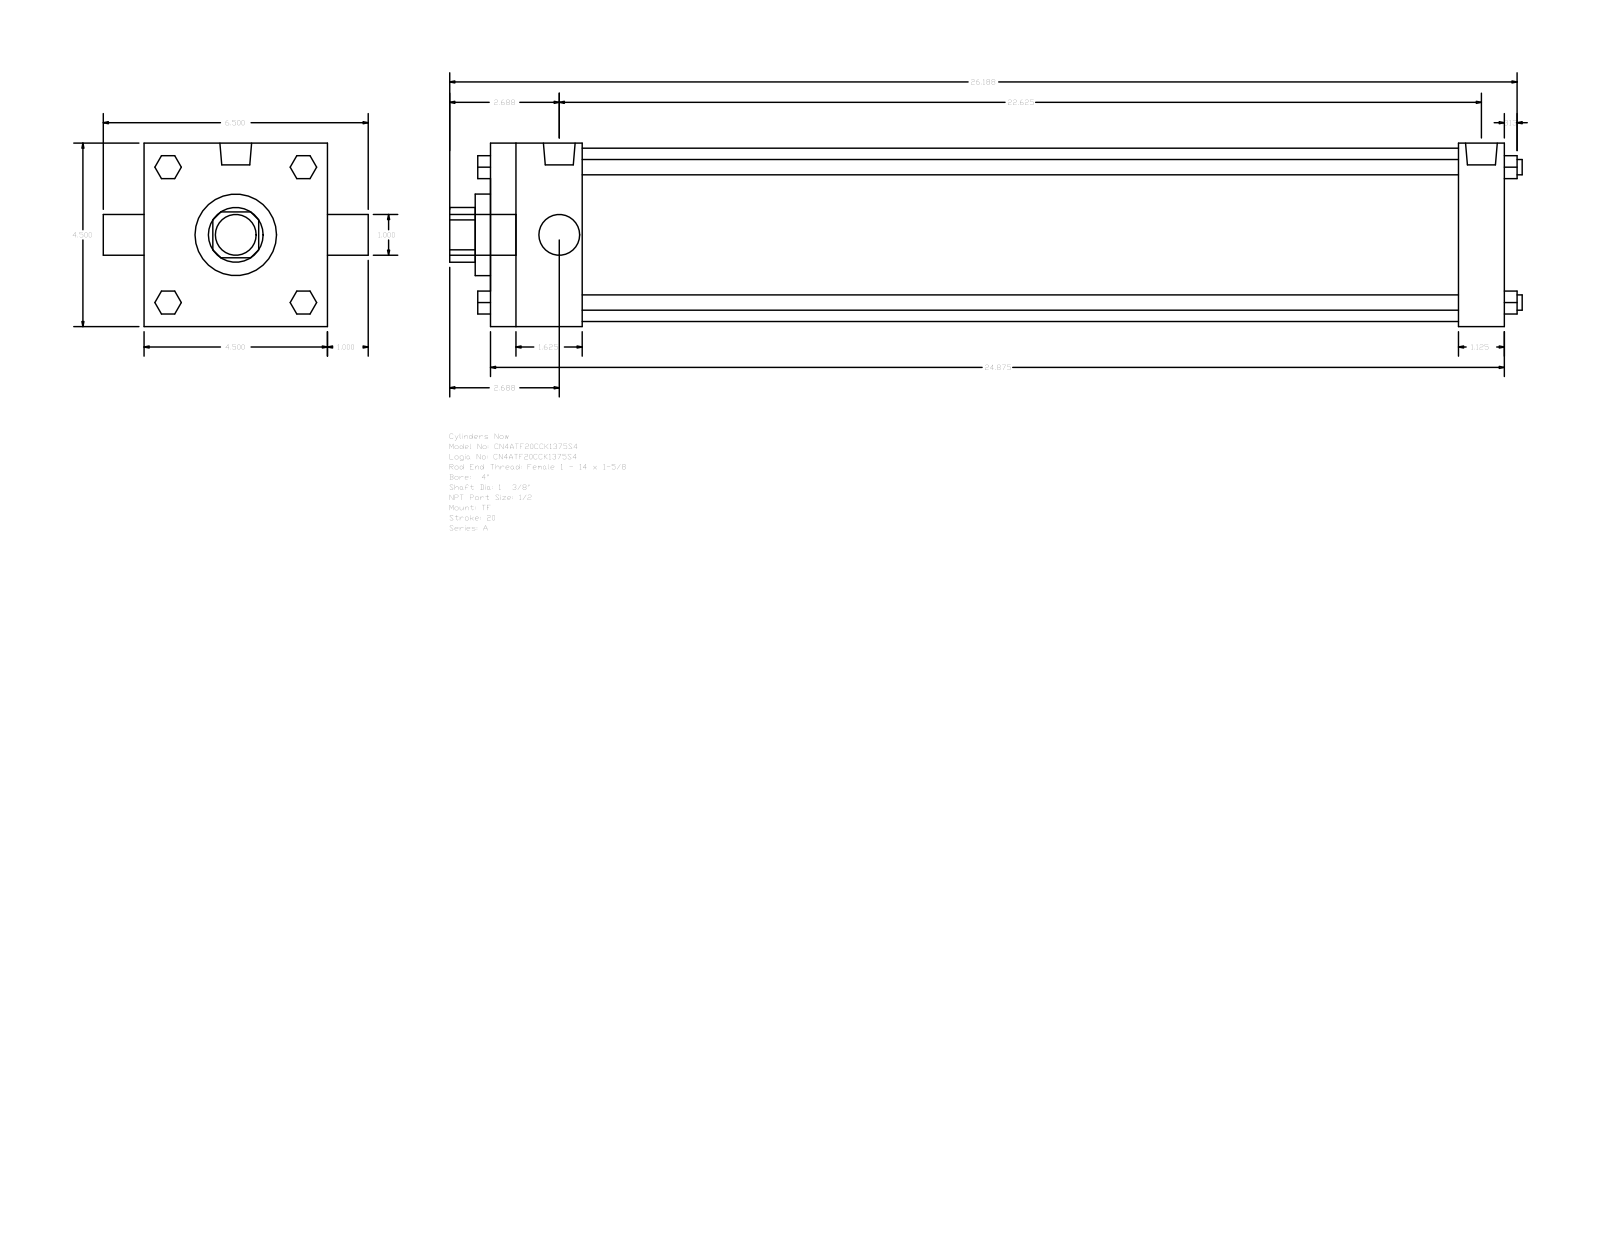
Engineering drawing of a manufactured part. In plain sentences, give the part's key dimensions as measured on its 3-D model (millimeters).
The part is named "A_TF__0400_1.375". Its 3-D file was written by "GSSL Pune (CONFIG_CONTROL_DESIGN)". It is 0 solids with 120 faces: 92 planar, 28 cylindrical and 0 other. Overall it measures 668.34 by 165.1 by 114.3 millimeters. Round holes: 1 of diameter 25.4, 1 of diameter 34.92, 1 of diameter 50.8, 1 of diameter 107.95. Round bosses or shafts: 4 of diameter 9.53, 3 of diameter 8.73, 2 of diameter 19.77, 1 of diameter 25.4. Partial cylindrical surfaces (rounded edges, fillets, slot ends): 1 of radius 17.06. The main face-to-face distances are 114.3, 631.83, 28.58, 603.25, 57.15, 546.1, 574.68, 14.29, 25.4, 9.52.
